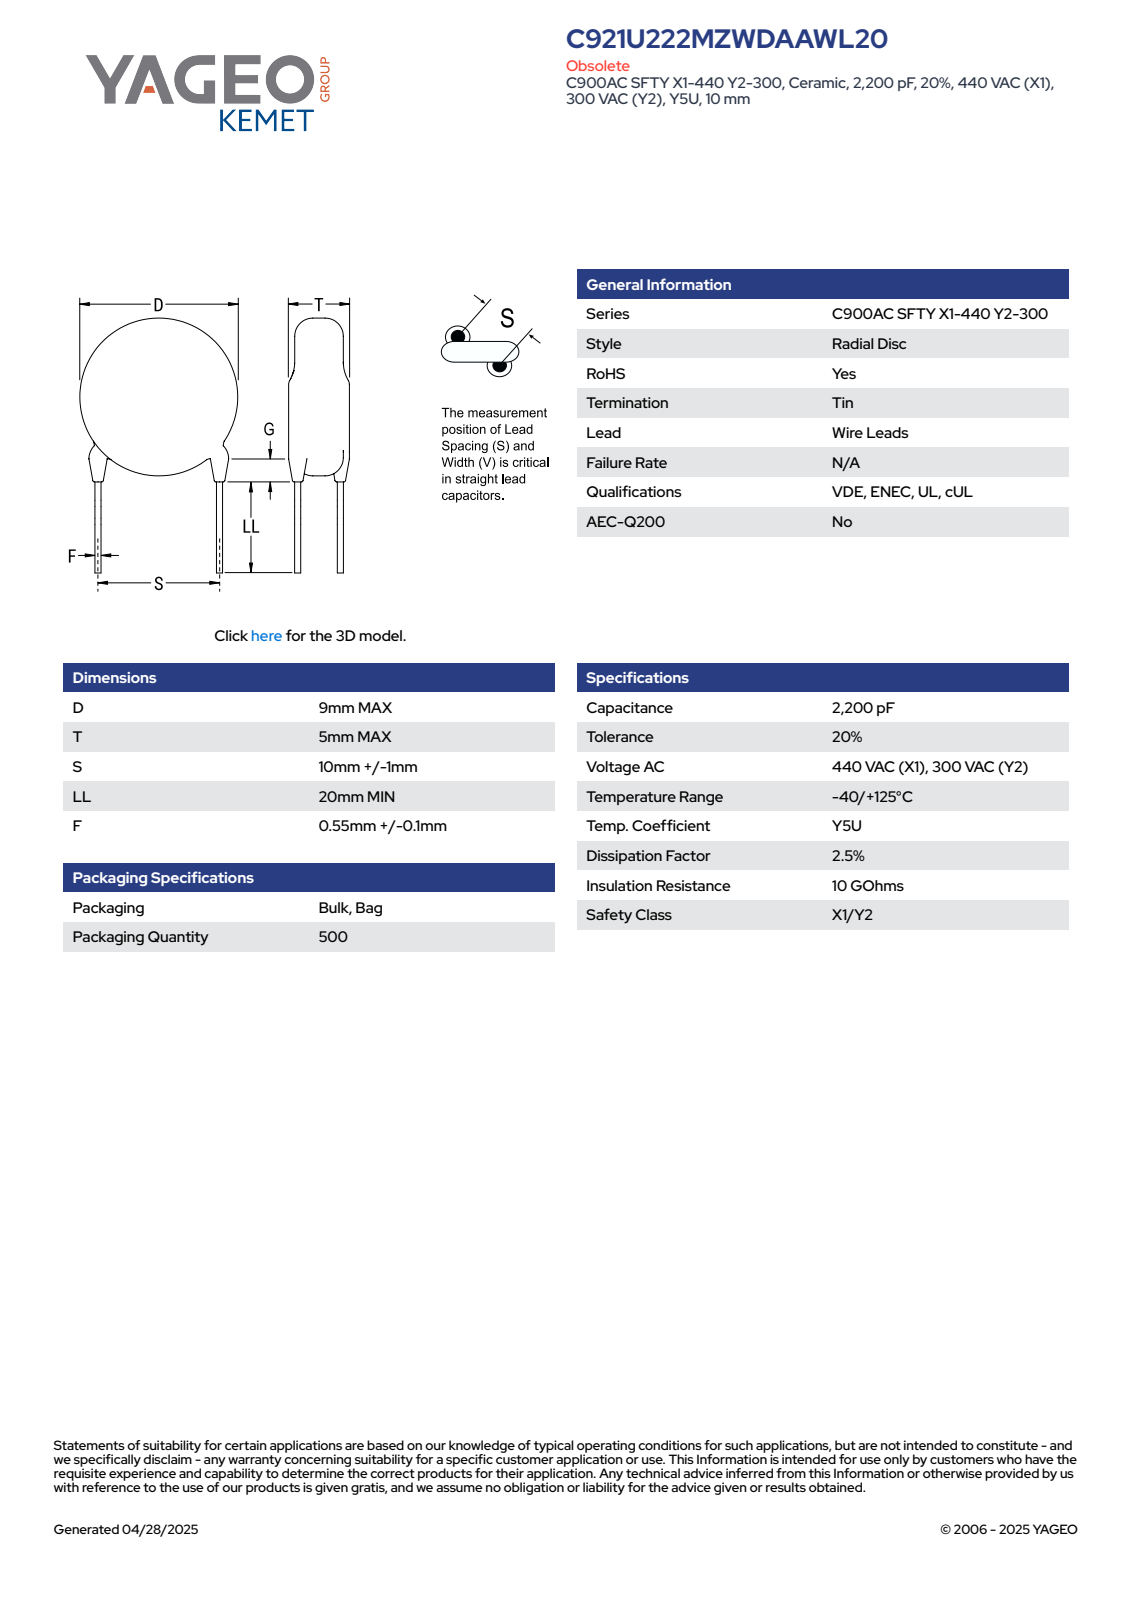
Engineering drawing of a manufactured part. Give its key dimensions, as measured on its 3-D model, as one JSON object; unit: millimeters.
{"part_name": "CCD_STC900_D9T5S10LL20F0.65G3", "step_written_by": "SolidWorks 2014 (AUTOMOTIVE_DESIGN)", "units": "millimeters", "bodies": {"solids": 4, "faces": 83, "planar": 61, "cylindrical": 6, "other": 16}, "overall_size": [29.39, 10.32, 5], "volume_mm3": 324, "surface_area_mm2": 346, "round_bosses_or_shafts": [[0.65, 2], [9, 1]], "face_to_face_distances": [5, 1.04, 25.41, 24.37, 0.84, 0.45, 0.39, 2.14, 3.08, 3.2]}
